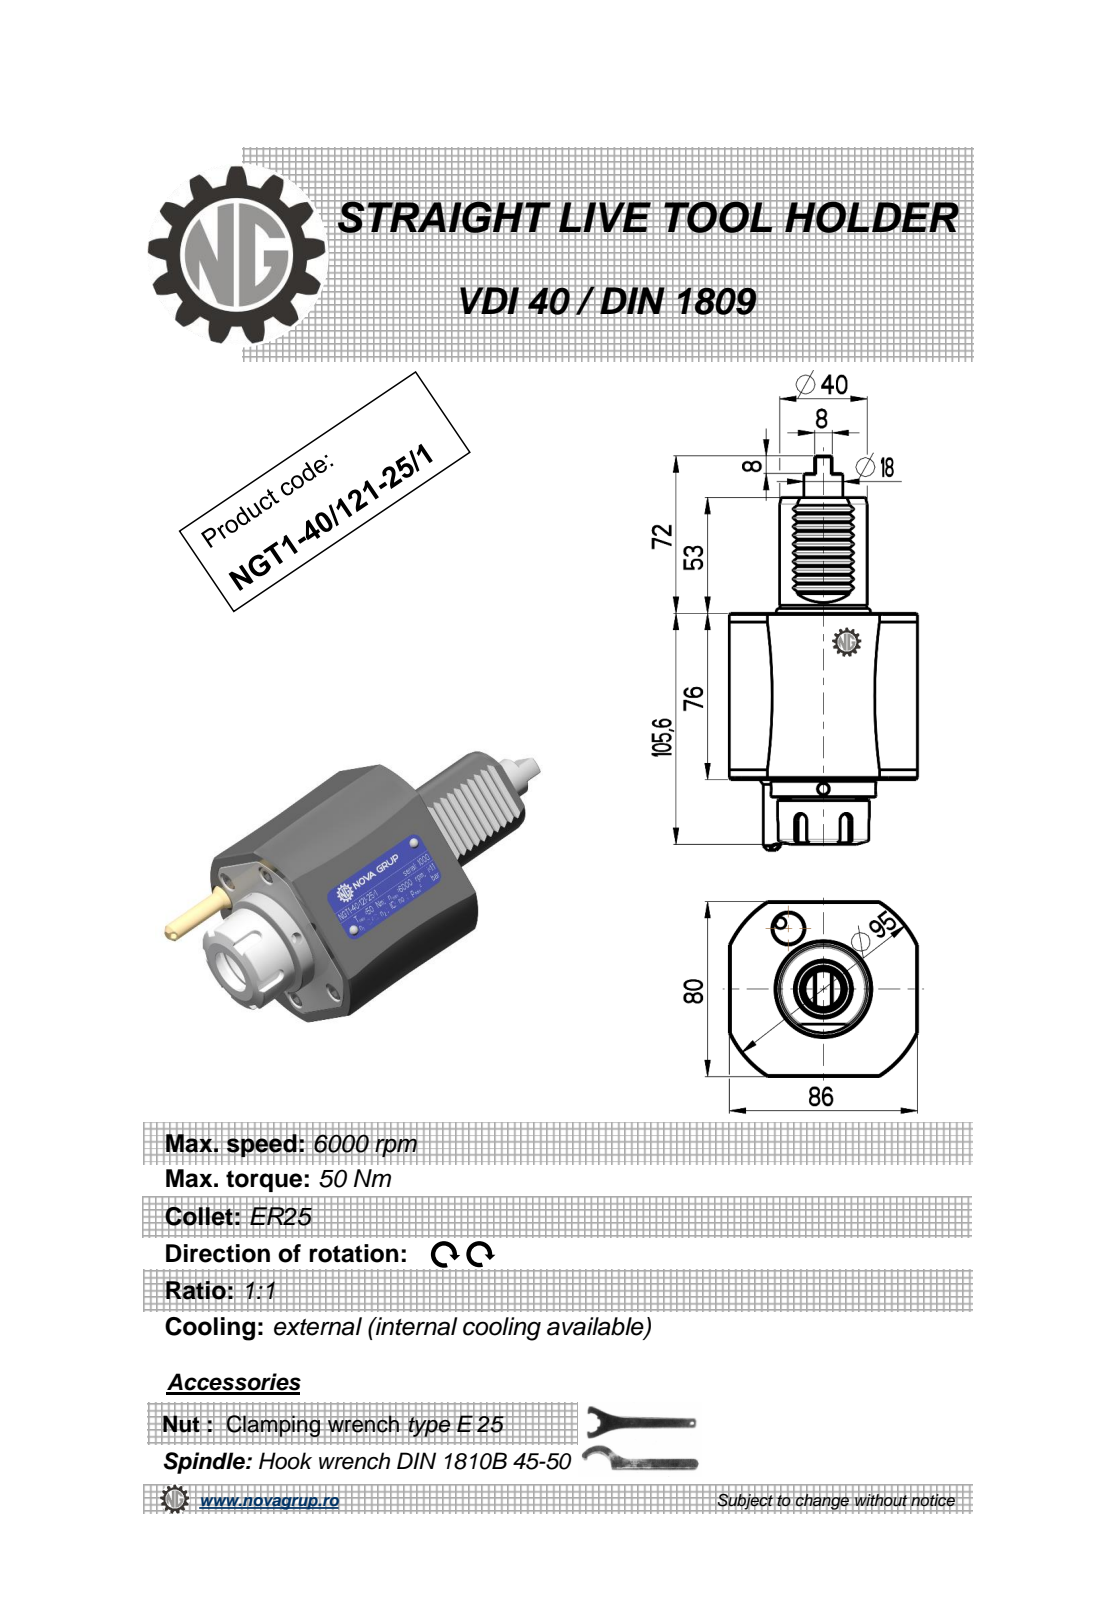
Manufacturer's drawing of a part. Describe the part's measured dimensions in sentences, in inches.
The part is named "NGT1_40_121_25_1". Its 3-D file was written by "PRO/ENGINEER BY PARAMETRIC TECHNOLOGY CORPORATION, 2010280 (CONFIG_CONTROL_DESIGN)". It is 1 solid with 265 faces: 102 planar, 58 cylindrical and 105 other. Overall it measures 7.1 by 3.386 by 3.213 inches. Its volume is 35.51 cubic inches and its surface area 78.8 square inches. Round holes: 3 of diameter 0.197, 1 of diameter 0.118. Round bosses or shafts: 1 of diameter 1.89, 1 of diameter 1.654, 1 of diameter 1.634, 1 of diameter 1.575, 1 of diameter 1.299, 1 of diameter 0.701, 1 of diameter 0.315. Partial cylindrical surfaces (rounded edges, fillets, slot ends): 10 of radius 0.012, 6 of radius 0.009, 5 of radius 0.118, 2 of radius 0.031, 1 of radius 1.87. The main face-to-face distances are 2.992, 3.15, 3.386, 0.315, 3.307, 0.111, 2.087, 5.079, 5.394, 0.223.
